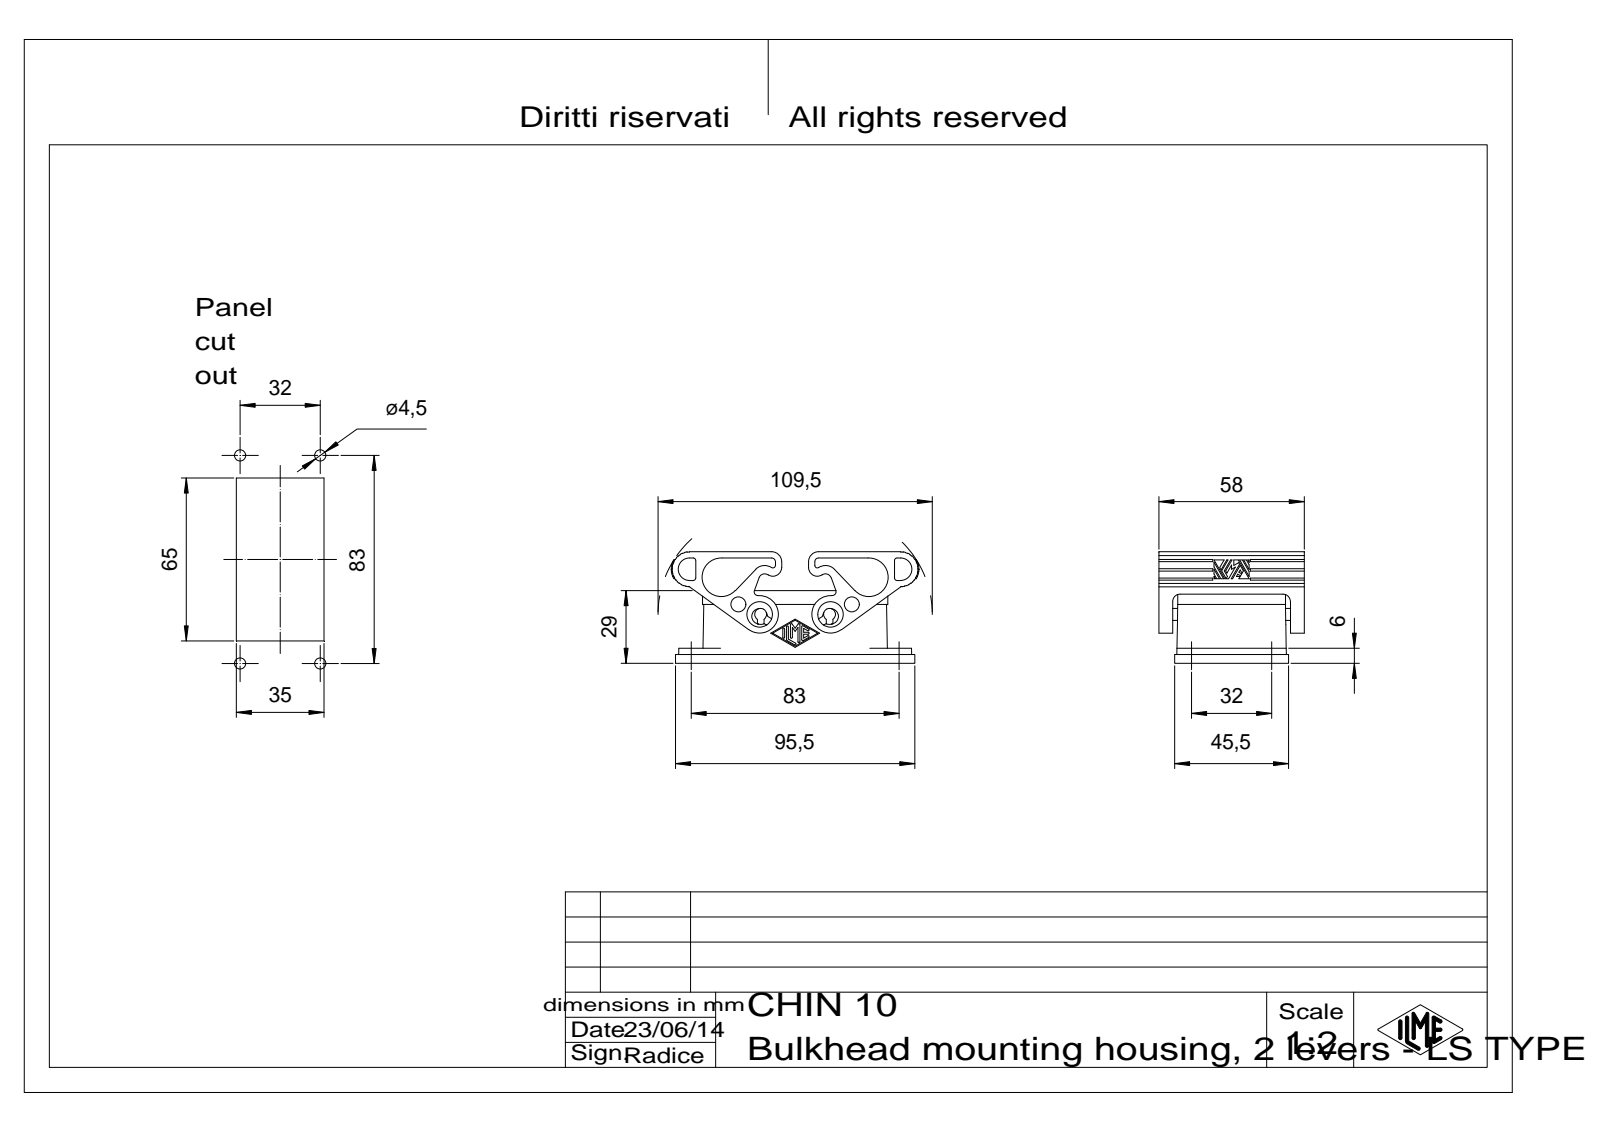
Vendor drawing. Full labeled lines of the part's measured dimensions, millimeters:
Part name (STEP PRODUCT): CHIN_10
STEP written by: CoCreate Modeling 16.00A 16-Aug-2008 (C) Parametric Technology GmbH (AUTOMOTIVE_DESIGN)
Units: millimetres
Bodies: 1 solid, 898 faces (436 planar, 344 cylindrical, 118 other)
Overall size (bounding box): 97.94 × 58 × 45.07
Volume: 55 260 mm³ · Surface area: 35 221 mm²
Round holes (diameter × count): ⌀4.75 ×4, ⌀6 ×2, ⌀10.2 ×2, ⌀6.2 ×1
Round bosses / shafts (diameter × count): ⌀6 ×2, ⌀4.8 ×2
Partial cylindrical surfaces — rounded edges, fillets, slot ends (radius × count): R0.8 ×20, R1 ×16, R0.9 ×12, R4 ×12, R3 ×8, R5 ×8, R7 ×6, R0.2 ×4
Main face-to-face distances: 5.5, 52.5, 47, 2.5, 3, 55.5, 50, 6, 0.63, 29
Hole centre spacings: 9.39, 32, 83, 88.96, 0.8, 9.76, 27.34, 27.35
